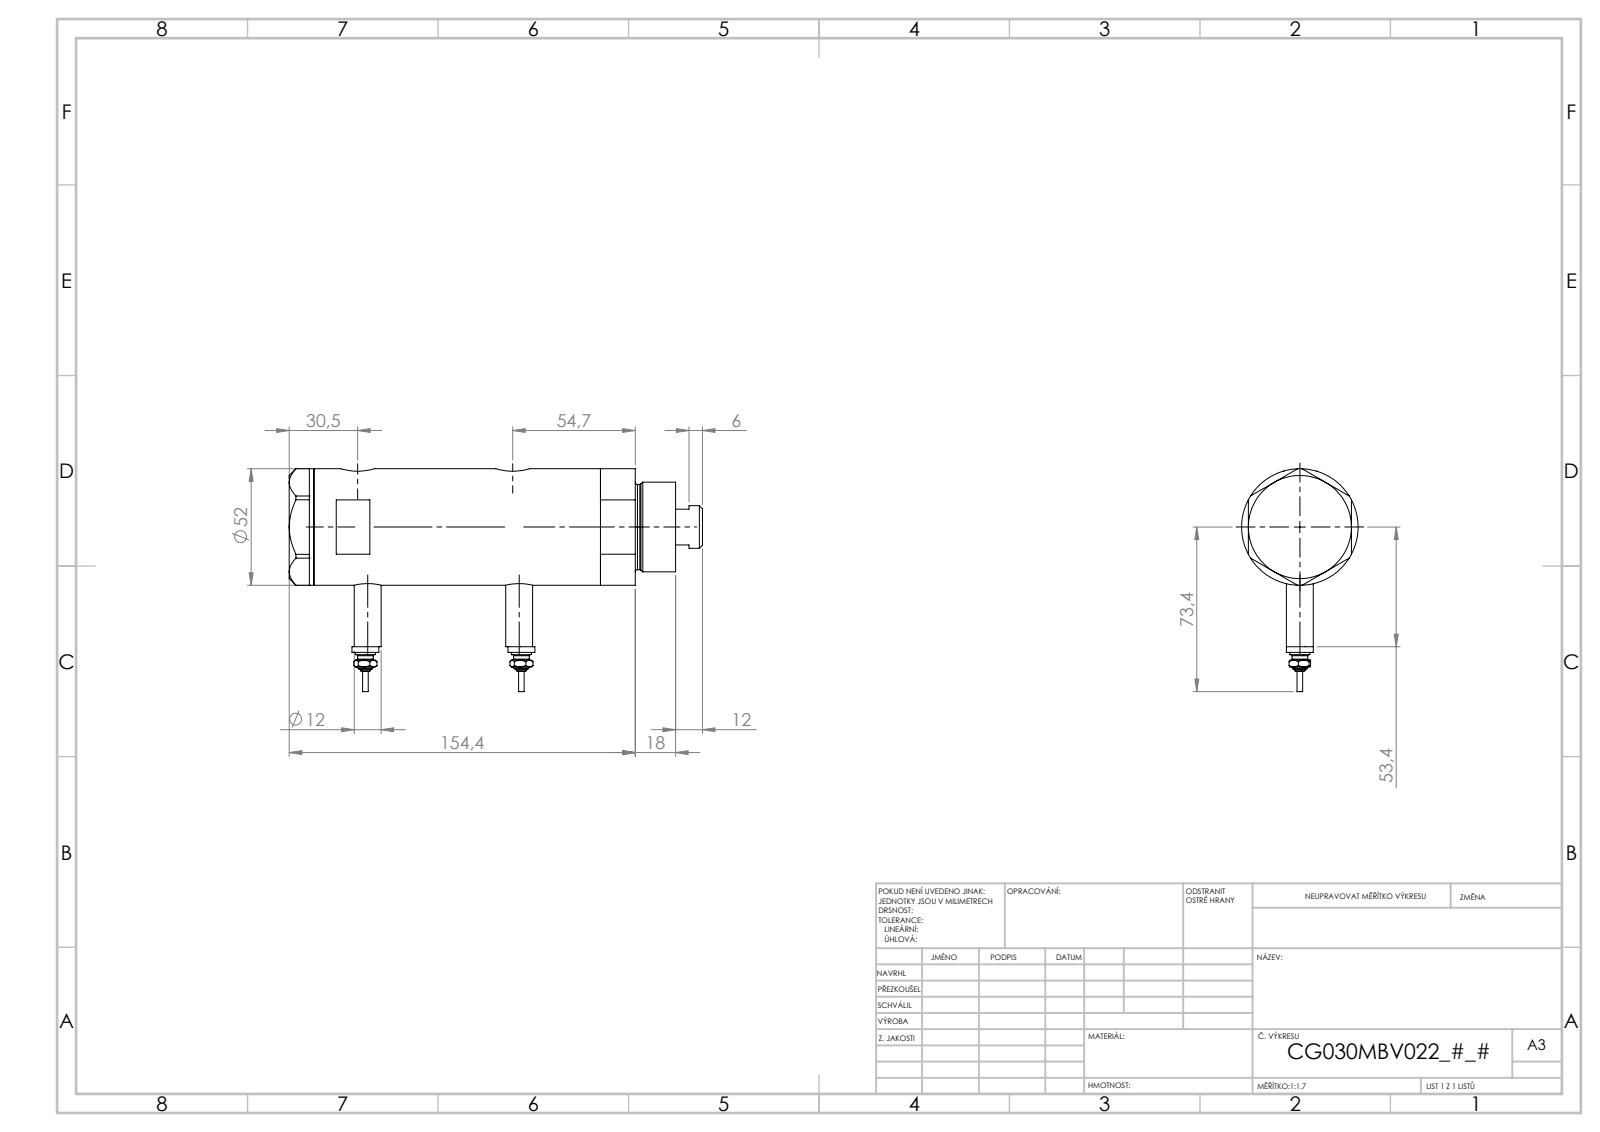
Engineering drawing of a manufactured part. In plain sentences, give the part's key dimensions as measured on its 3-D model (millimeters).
The part is named "V270CG_BACK; V270CG_VC; Switch; V270CG_FRONT (+1 more)". Its 3-D file was written by "SolidWorks 2019 (CONFIG_CONTROL_DESIGN)". It is 6 solids with 226 faces: 93 planar, 69 cylindrical and 64 other. Overall it measures 184.4 by 99.4 by 52 millimeters. Its volume is 344 076 cubic millimeters and its surface area 80 164 square millimeters. Round holes: 2 of diameter 9.73, 2 of diameter 12.5, 2 of diameter 15, 1 of diameter 6.5, 1 of diameter 20, 1 of diameter 21.5, 1 of diameter 30, 1 of diameter 33, 1 of diameter 44. Round bosses or shafts: 4 of diameter 12, 2 of diameter 9, 2 of diameter 7, 2 of diameter 4.5, 2 of diameter 2.5, 1 of diameter 52, 1 of diameter 40, 1 of diameter 38. The main face-to-face distances are 91.5, 23.8, 67.7, 11, 34.8, 102.5, 46, 36.4, 138.9, 127.9. The hole center spacings are 2.9, 4.5, 64.7, 67.6, 69.2, 72.1.
